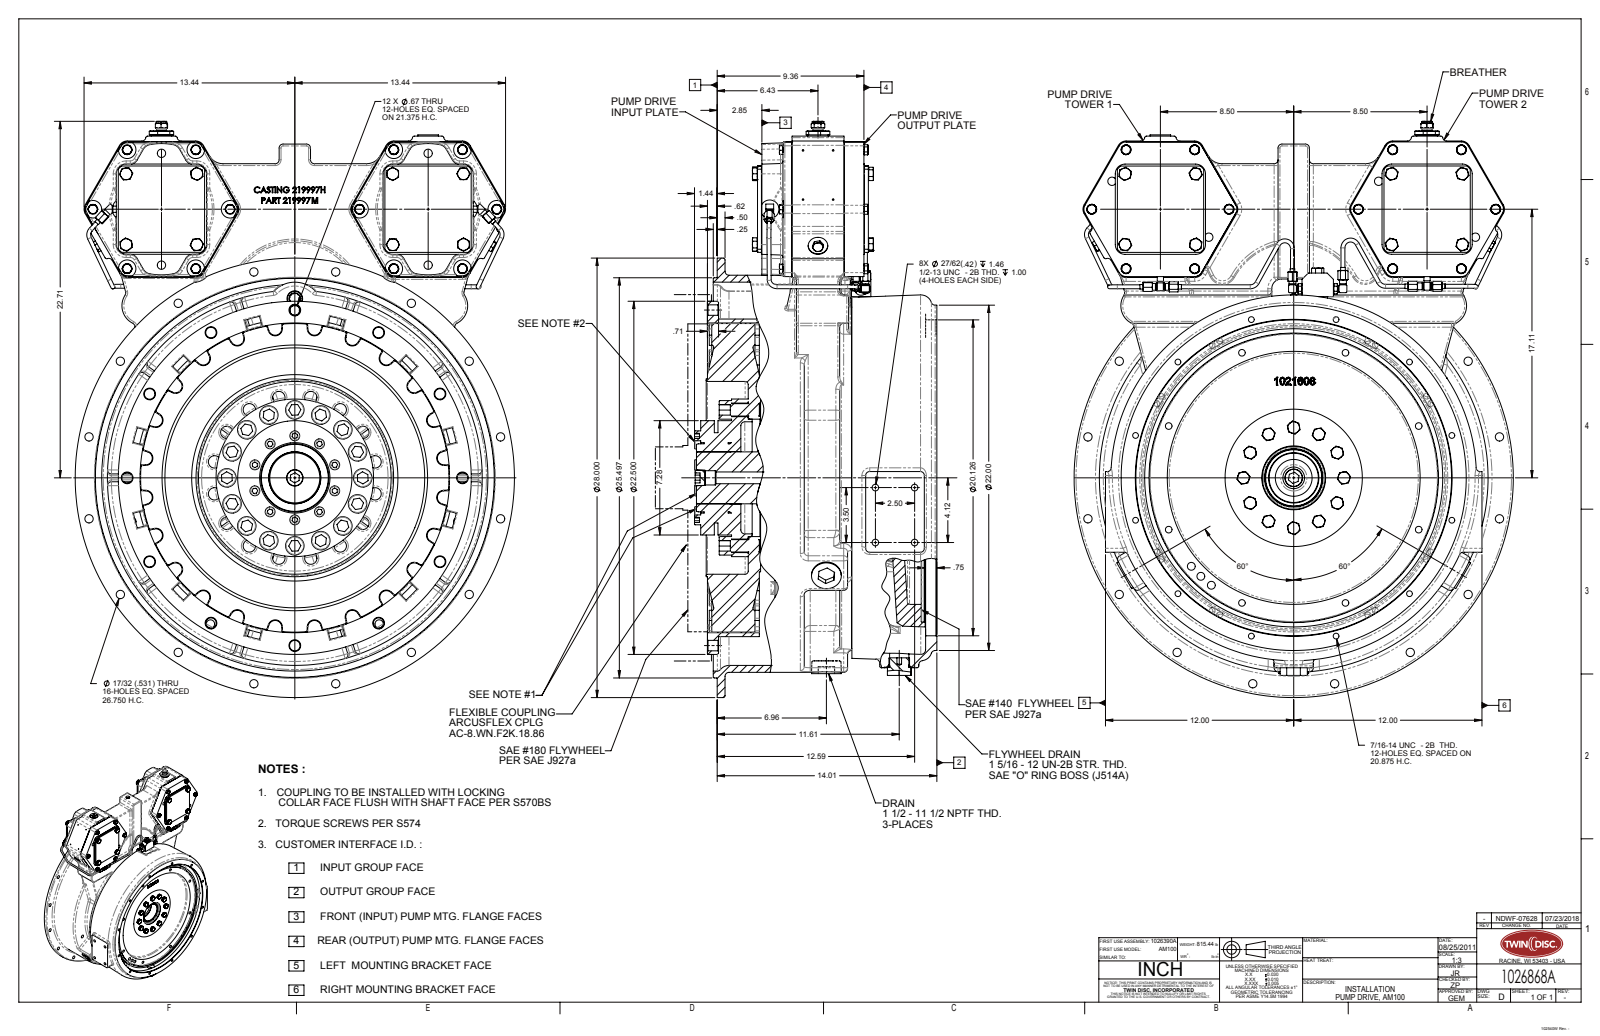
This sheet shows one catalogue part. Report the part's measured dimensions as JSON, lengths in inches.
{"part_name": "1026868A", "step_written_by": "SolidWorks 2015 (AUTOMOTIVE_DESIGN)", "units": "inches", "bodies": {"solids": 0, "faces": 3253, "planar": 1243, "cylindrical": 976, "other": 1034}, "overall_size": [36.711, 28, 15.45], "round_holes": [[0.531, 20], [0.368, 12], [0.422, 12], [0.669, 12], [0.787, 8], [0.437, 6], [0.53, 4], [0.531, 4], [0.5, 3], [0.107, 2], [1.18, 2], [1.25, 2]], "round_bosses_or_shafts": [[0.743, 17], [1.181, 16], [0.557, 14], [0.25, 13], [0.63, 10], [0.62, 9], [0.296, 7], [0.437, 6]], "partial_cylinders_radius": [[0.12, 80], [0.25, 79], [0.05, 62], [0.1, 48], [0.5, 28], [0.42, 24], [0.56, 21], [0.459, 17]], "face_to_face_distances": [0.5, 5.05, 3.539, 8.589, 4.55, 8.089, 9.209, 5.67, 1.12, 0.62], "hole_center_spacings": [5.219, 10.237, 13.375, 14.861, 22.242, 24.713, 18.915, 26.235]}
